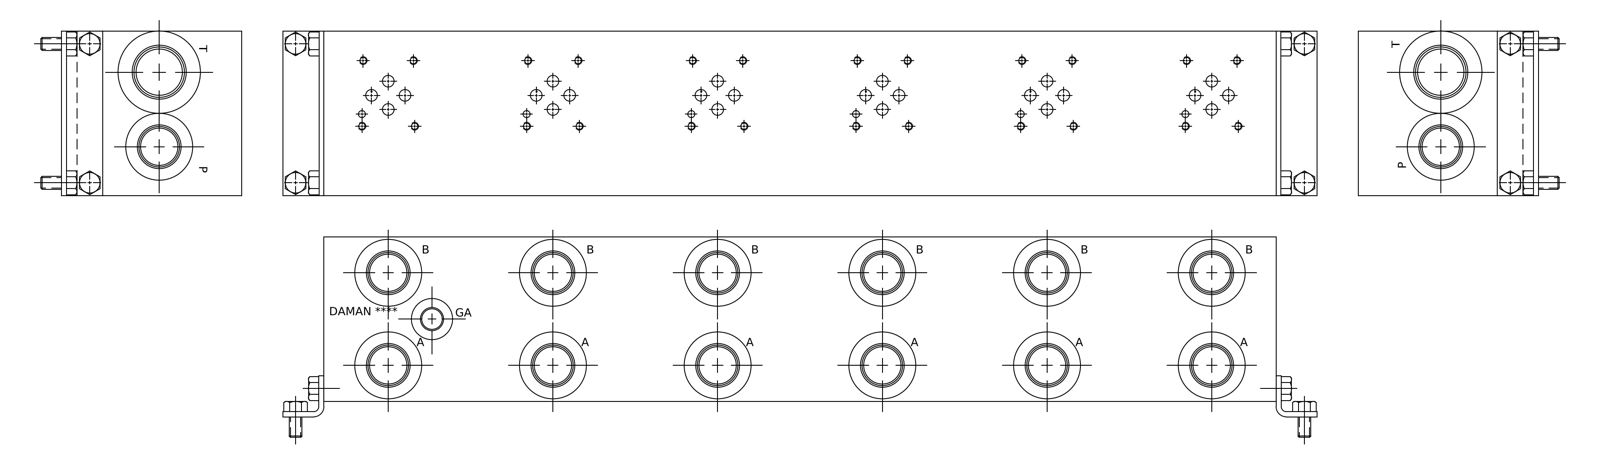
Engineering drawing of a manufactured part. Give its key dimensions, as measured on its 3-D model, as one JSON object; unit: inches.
{"part_name": "C:\\\\Program Files\\\\PARO\\\\Hydroman 800\\\\Export\\\\AD03HP064S", "step_written_by": "Autodesk Inventor 2012 (AUTOMOTIVE_DESIGN)", "units": "inches", "bodies": {"solids": 1, "faces": 360, "planar": 85, "cylindrical": 177, "other": 98}, "overall_size": [23.125, 4, 4], "volume_in3": 343.6, "surface_area_in2": 517.3, "round_holes": [[0.149, 24], [0.19, 24], [0.281, 24], [0.906, 13], [0.981, 13], [1.15, 13], [1.614, 13], [1.063, 8], [0.422, 7], [0.156, 6], [1.063, 5], [0.257, 2]], "face_to_face_distances": [4, 0.03, 3.97, 23.125, 0.161, 23.095, 0.03, 23.065, 23.095, 0.781], "hole_center_spacings": [4, 8, 4.589, 8.31, 1.594, 2.026, 0.532, 0.533]}
